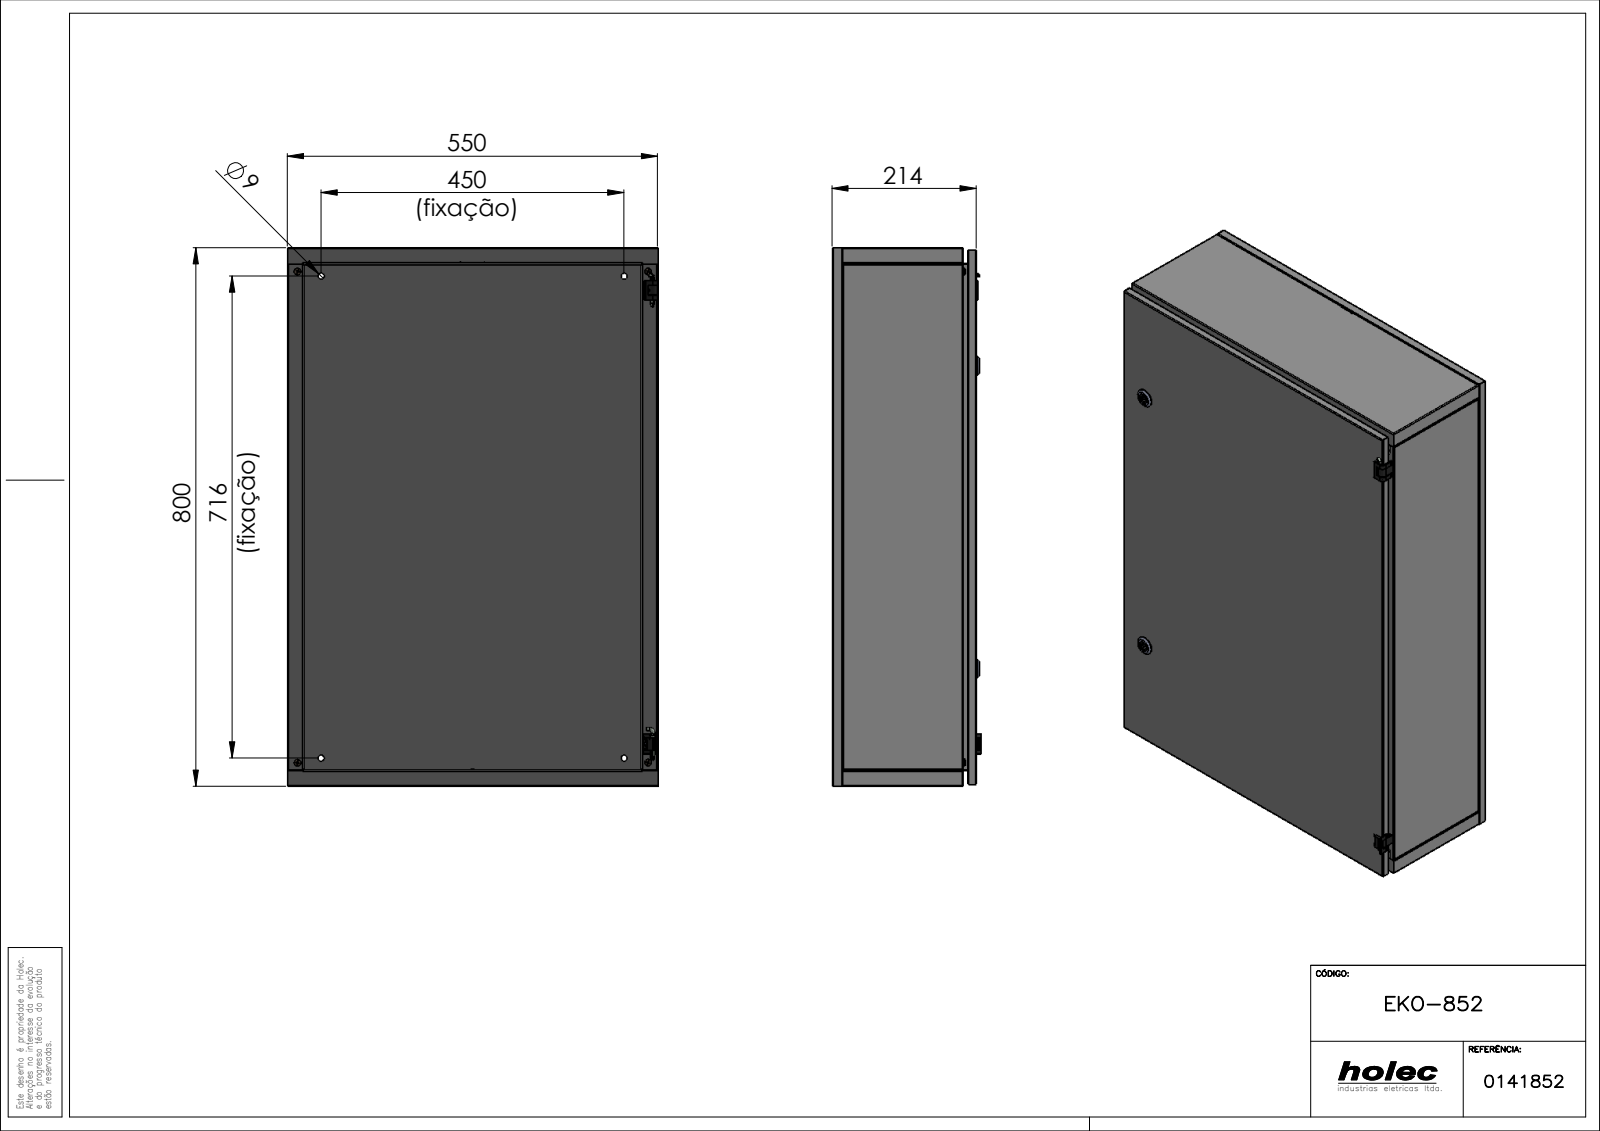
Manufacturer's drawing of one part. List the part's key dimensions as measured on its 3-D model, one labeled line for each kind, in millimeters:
Part name (STEP PRODUCT): EKO-852
STEP written by: SolidWorks 2017 (AUTOMOTIVE_DESIGN)
Units: millimetres
Bodies: 70 solids, 3128 faces (1524 planar, 956 cylindrical, 648 other)
Overall size (bounding box): 800 × 550 × 220.88
Volume: 1 833 000 mm³ · Surface area: 3 605 000 mm²
Round holes (diameter × count): ⌀4.3 ×24, ⌀4.2 ×19, ⌀6 ×18, ⌀7.52 ×10, ⌀1.8 ×9, ⌀5.5 ×6, ⌀11 ×6, ⌀5 ×4, ⌀9 ×4, ⌀3.3 ×2, ⌀4 ×2, ⌀4.1 ×2
Round bosses / shafts (diameter × count): ⌀10 ×10, ⌀7 ×10, ⌀5 ×10, ⌀3.2 ×9, ⌀28 ×2, ⌀19 ×2, ⌀15.7 ×2, ⌀15 ×2
Partial cylindrical surfaces — rounded edges, fillets, slot ends (radius × count): R0.2 ×88, R1.5 ×50, R0.5 ×48, R0.3 ×20, R1 ×16, R2.5 ×10, R2 ×6, R1.05 ×4
Main face-to-face distances: 1, 213.1, 214.1, 212.1, 549, 799, 550, 548, 24, 22.9
Hole centre spacings: 25, 50, 75, 230.5, 249.5, 31.4, 231.8, 231.91
